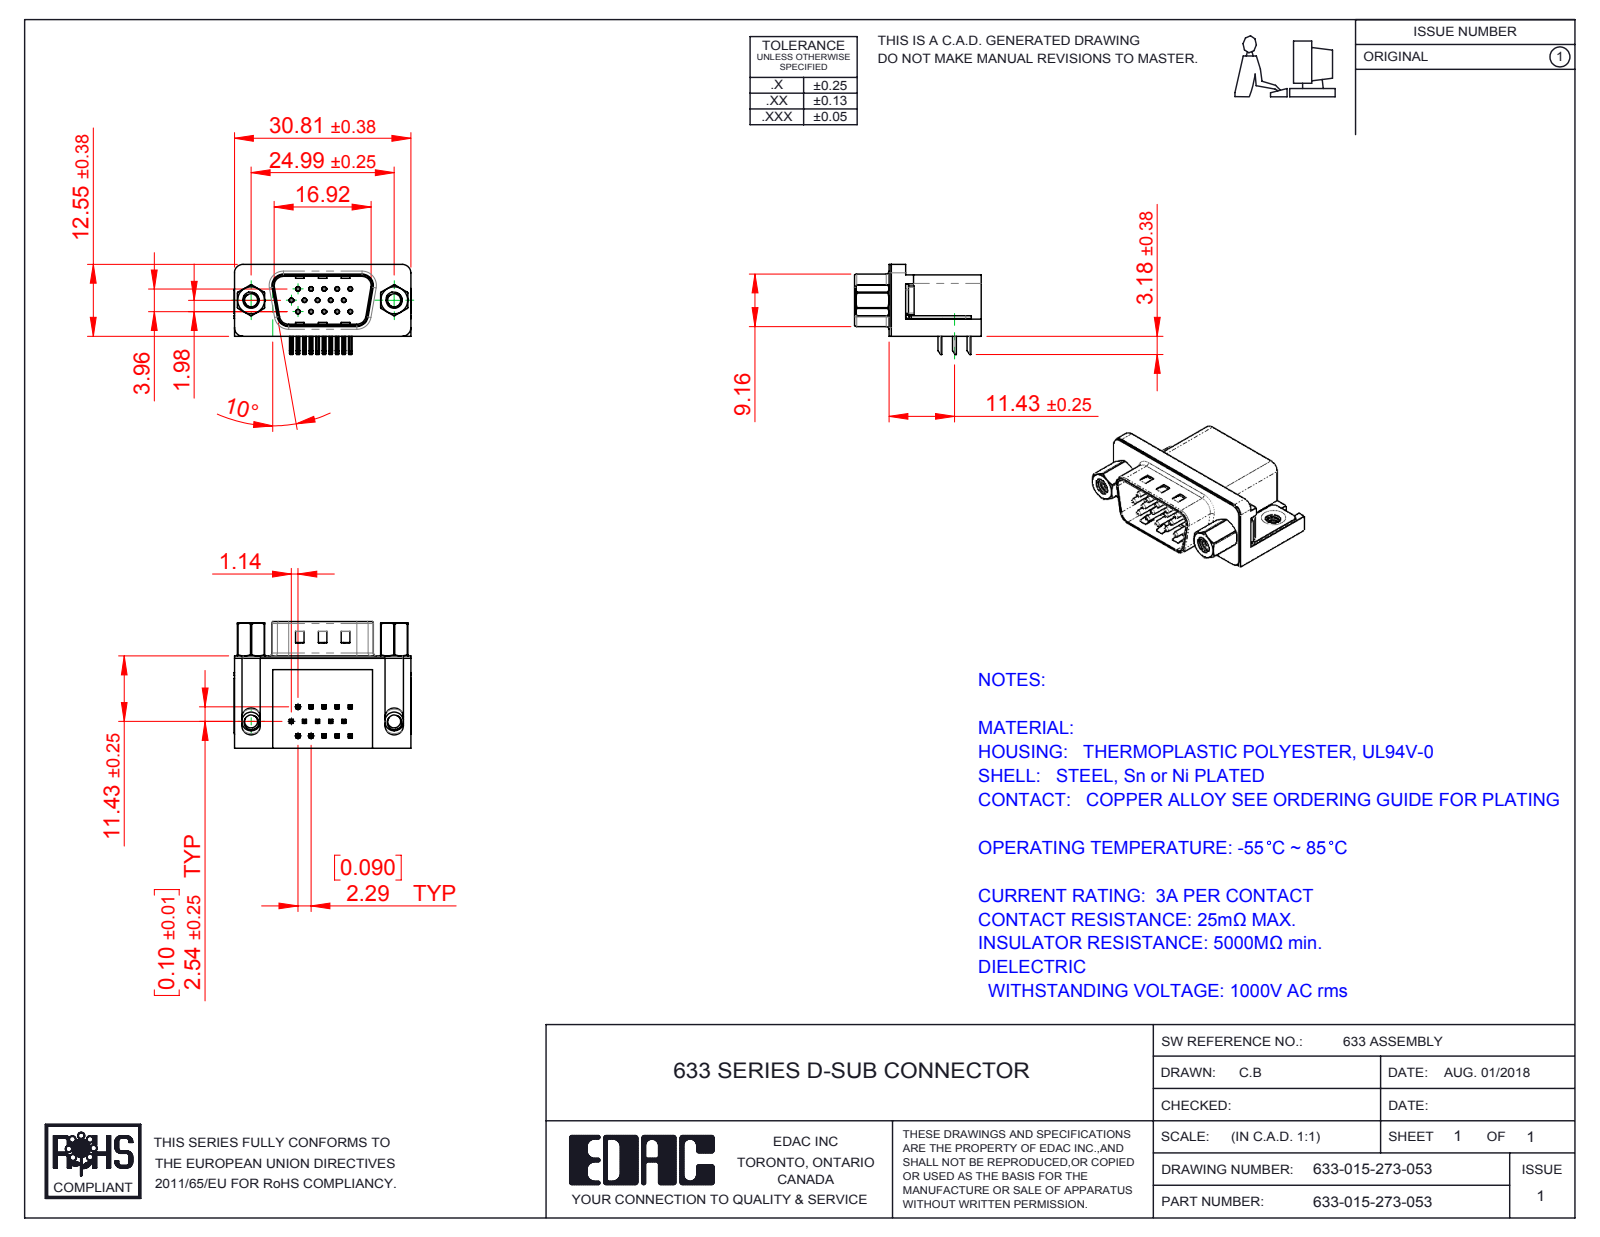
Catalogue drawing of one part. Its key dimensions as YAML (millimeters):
part_name: "633-015-273-053; 633 Housing_15 Contact; 633 Contact Middle; 633 Contact Bottom (+6 more)"
step_written_by: "SolidWorks 2016 (CONFIG_CONTROL_DESIGN)"
units: millimeters
bodies: {solids: 23, faces: 1593, planar: 883, cylindrical: 519, other: 191}
overall_size: [30.89, 22.1, 15.73]
volume: 4287
surface_area: 5954
round_holes:
  - {diameter: 0.35, count: 15}
  - {diameter: 0.8, count: 15}
  - {diameter: 2.26, count: 4}
  - {diameter: 2.29, count: 2}
  - {diameter: 4, count: 2}
  - {diameter: 4.8, count: 2}
  - {diameter: 5, count: 2}
round_bosses_or_shafts:
  - {diameter: 0.75, count: 15}
  - {diameter: 4.9, count: 2}
  - {diameter: 4.75, count: 2}
  - {diameter: 3.9, count: 2}
  - {diameter: 3.26, count: 2}
  - {diameter: 2.79, count: 2}
partial_cylinders:
  - {radius: 0.25, count: 68}
  - {radius: 0.12, count: 30}
  - {radius: 1, count: 16}
  - {radius: 0.5, count: 9}
  - {radius: 1.6, count: 8}
  - {radius: 1.5, count: 7}
  - {radius: 0.9, count: 4}
  - {radius: 2, count: 4}
face_to_face_distances: [0.4, 10.35, 15.7, 16.1, 2.9, 2.5, 0.5, 6.7, 0.35, 10.7]
hole_center_spacings: [3.96, 2.28, 4.57, 2.29, 6.05, 6.86, 7.92, 6.04]
